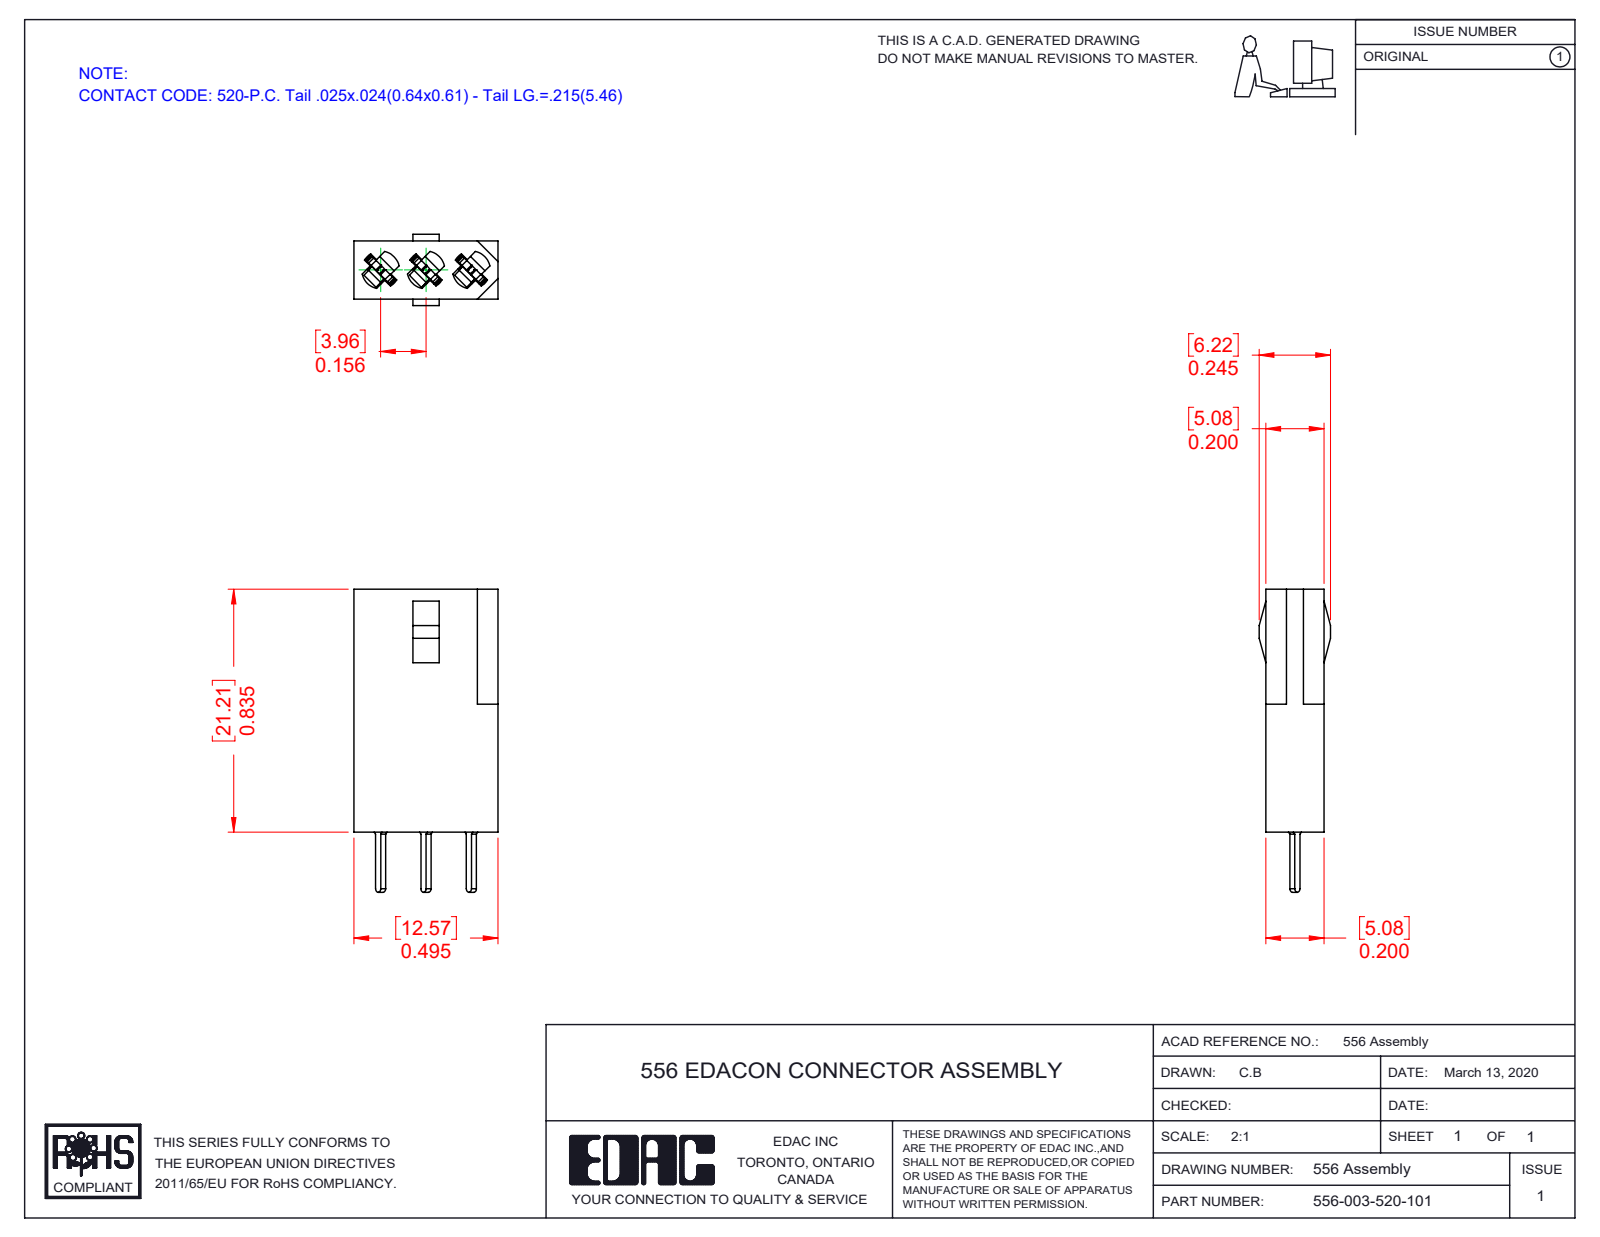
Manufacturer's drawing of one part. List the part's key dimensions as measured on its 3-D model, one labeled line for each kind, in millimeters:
Part name (STEP PRODUCT): 556-210-001_556-003-000-101; 516-292-001_520 Contact; 556-003-520-101
STEP written by: SolidWorks 2016 (CONFIG_CONTROL_DESIGN)
Units: millimetres
Bodies: 4 solids, 314 faces (200 planar, 90 cylindrical, 24 other)
Overall size (bounding box): 26.45 × 12.57 × 6.22
Volume: 974 mm³ · Surface area: 2 054 mm²
Round holes (diameter × count): ⌀1.27 ×3, ⌀3.35 ×3
Partial cylindrical surfaces — rounded edges, fillets, slot ends (radius × count): R0.3 ×12, R0.56 ×12, R0.18 ×6, R0.2 ×6, R0.41 ×6, R2.03 ×6, R0.32 ×3, R1.65 ×3
Main face-to-face distances: 2.8, 5.08, 5.6, 0.61, 3.41, 1.78, 0.68, 12.57, 0.76, 2.88
Hole centre spacings: 2.8, 3.96, 5.6, 7.92
